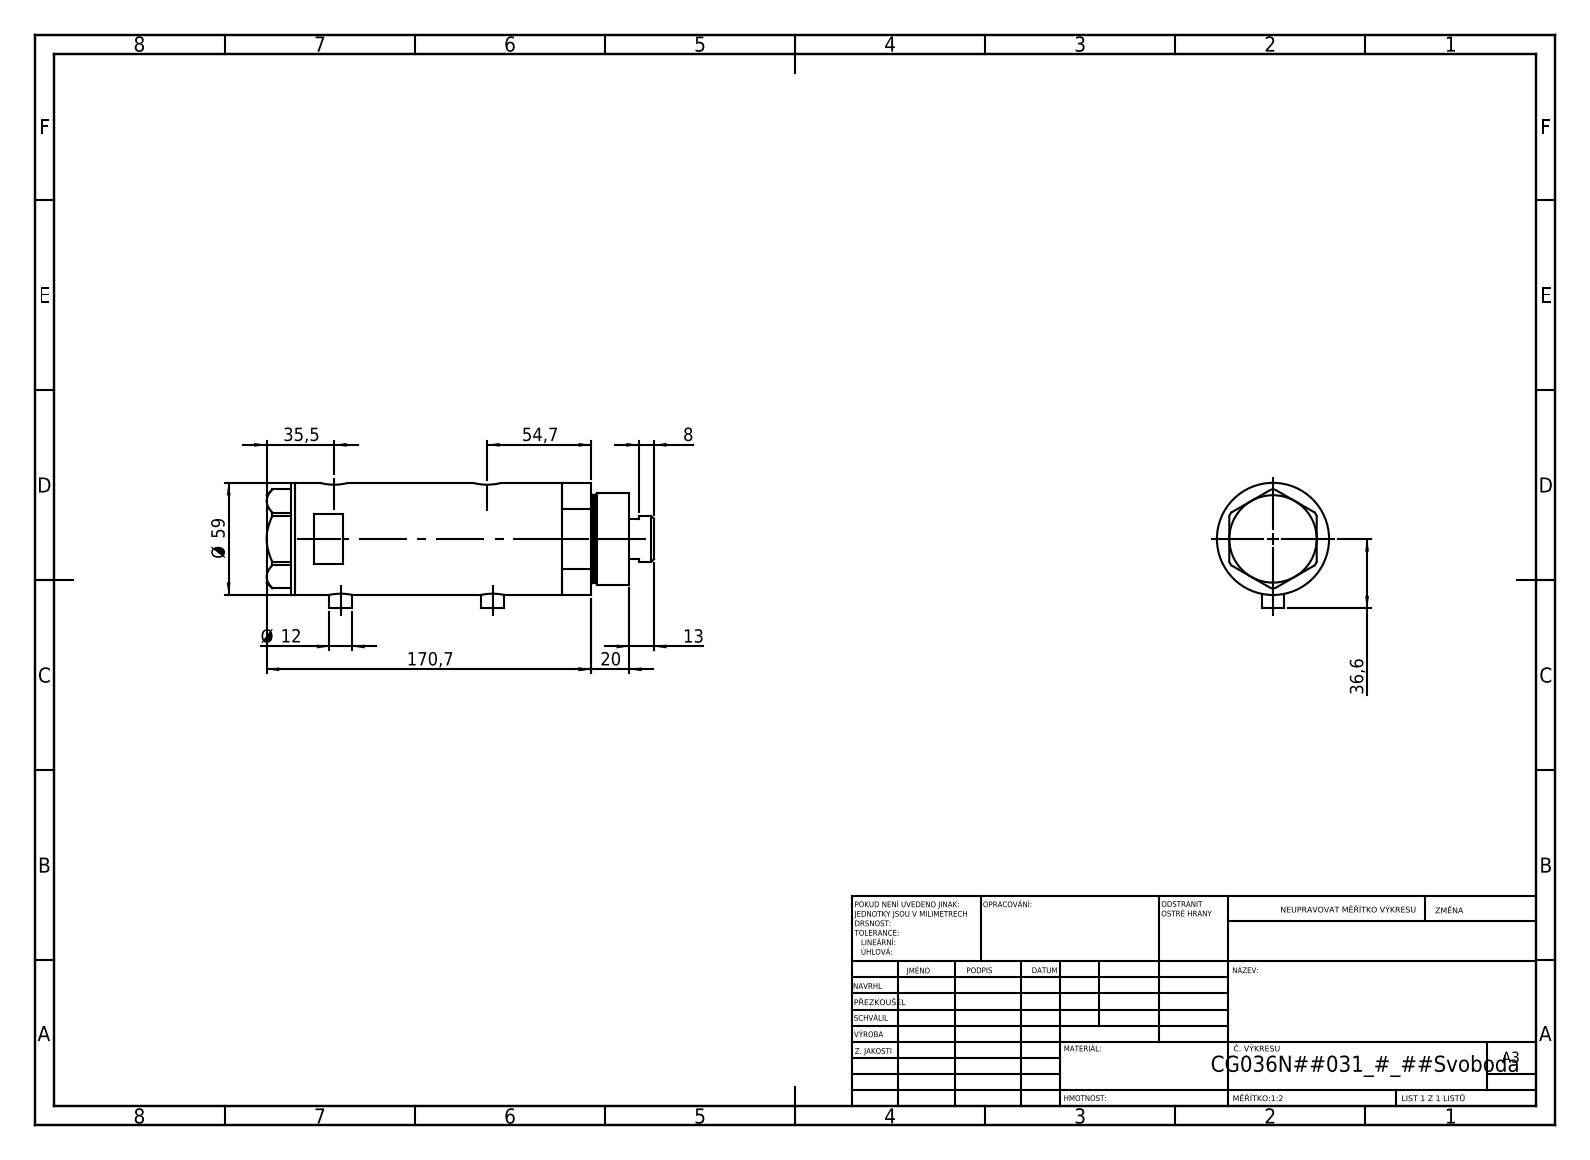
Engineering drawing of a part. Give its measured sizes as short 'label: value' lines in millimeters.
name: V270CG_MIDDLE; V270CG_BACK; V270CG_VC; V270CG_FRONT
written by: SolidWorks 2019 (CONFIG_CONTROL_DESIGN)
unit: mm
bodies: 4 solids, 126 faces (53 planar, 53 cylindrical, 20 other)
size: 203.8 × 66.1 × 59
volume: 471 960 mm³; area: 98 914 mm²
holes: 2× ⌀5, 2× ⌀9.73, 2× ⌀12.5, 2× ⌀15, 1× ⌀8.5, 1× ⌀25, 1× ⌀26.5, 1× ⌀36, 1× ⌀40, 1× ⌀52
bosses: 2× ⌀12, 1× ⌀59, 1× ⌀48, 1× ⌀46, 1× ⌀24
face distances: 102.2, 23.5, 78.7, 15, 38.5, 117.2, 2, 175.7, 190.7, 152.2
hole spacings: 2.9, 3.5, 77, 79.9, 80.5, 83.4
